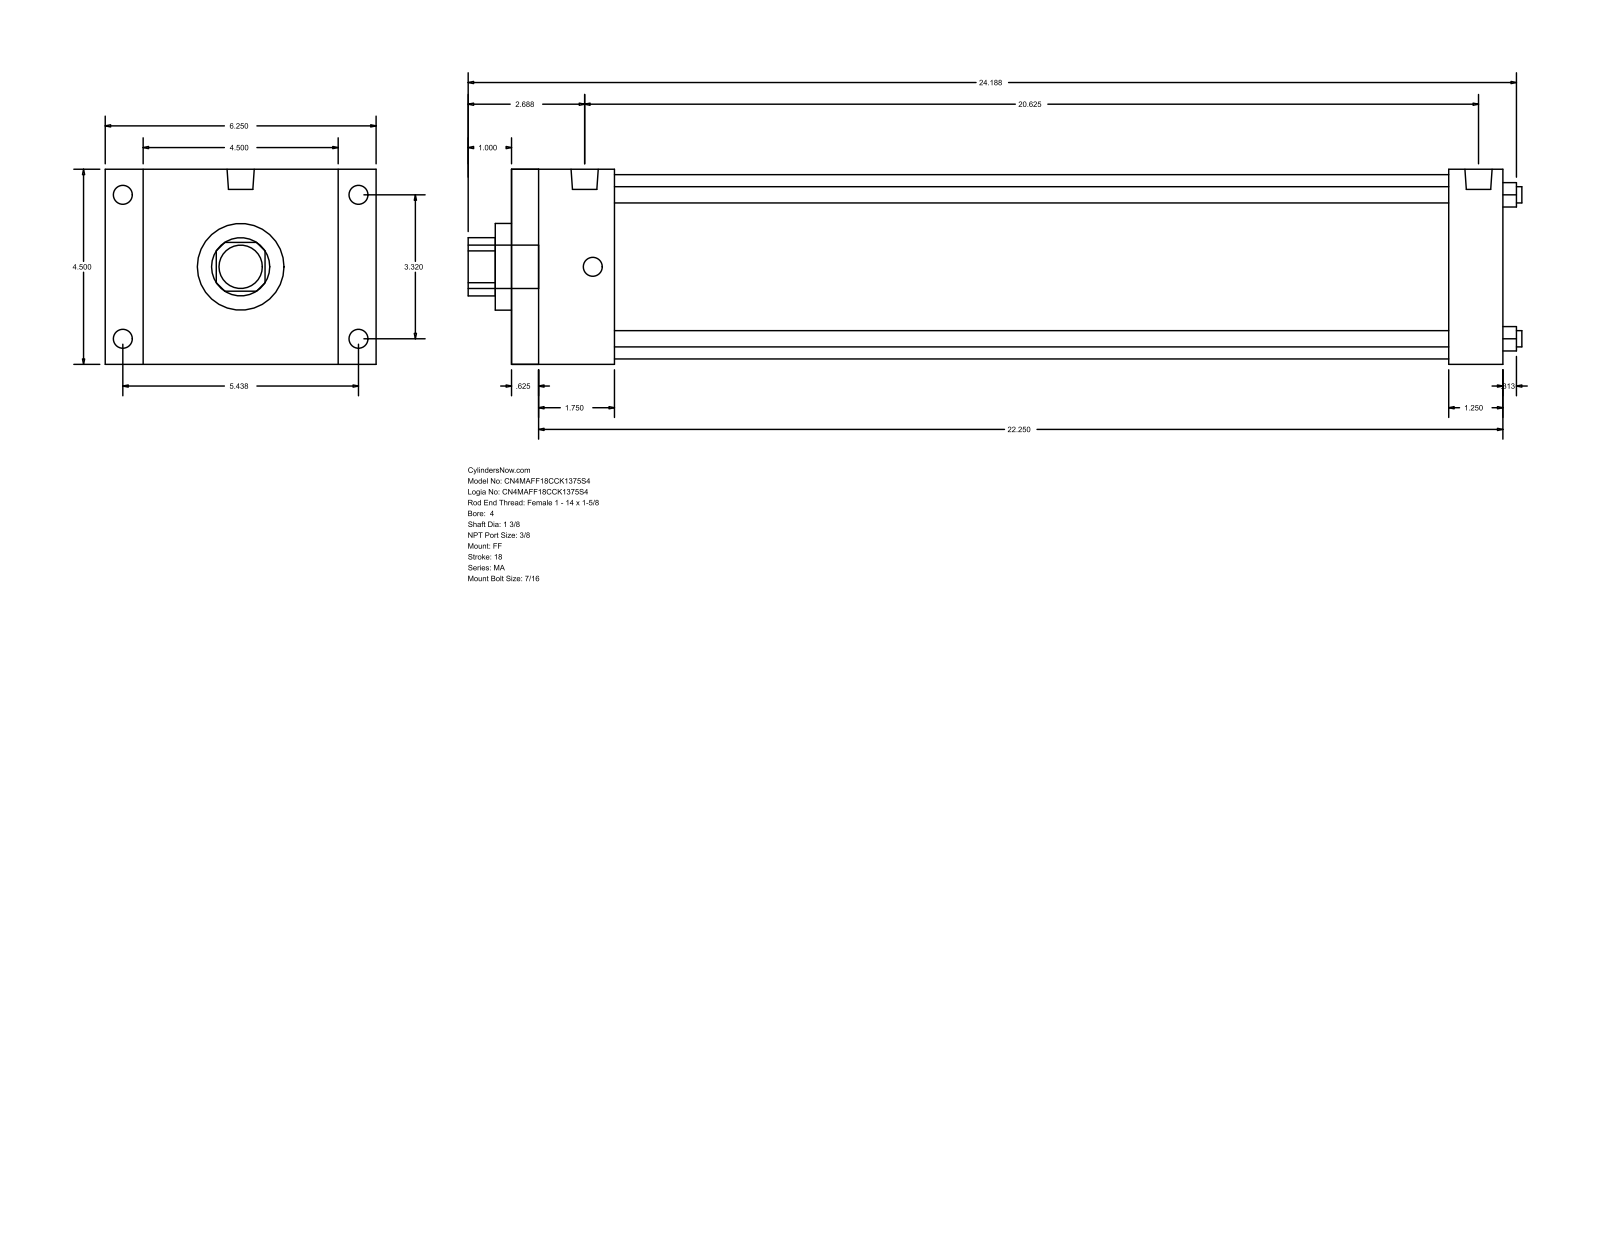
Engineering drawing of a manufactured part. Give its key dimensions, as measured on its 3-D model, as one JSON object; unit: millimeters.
{"part_name": "MA_FF__0400_1.375", "step_written_by": "GSSL Pune (CONFIG_CONTROL_DESIGN)", "units": "millimeters", "bodies": {"solids": 0, "faces": 92, "planar": 64, "cylindrical": 28, "other": 0}, "overall_size": [617.54, 158.75, 114.3], "round_holes": [[9.53, 4], [34.92, 1], [50.8, 1], [107.95, 1]], "round_bosses_or_shafts": [[11.11, 8], [15.93, 2], [25.4, 1]], "partial_cylinders_radius": [[17.06, 1]], "face_to_face_distances": [114.3, 581.02, 15.87, 565.15, 22.23, 136.53, 549.27, 533.4, 31.75, 60.32], "hole_center_spacings": [59.62, 84.32, 119.25]}
